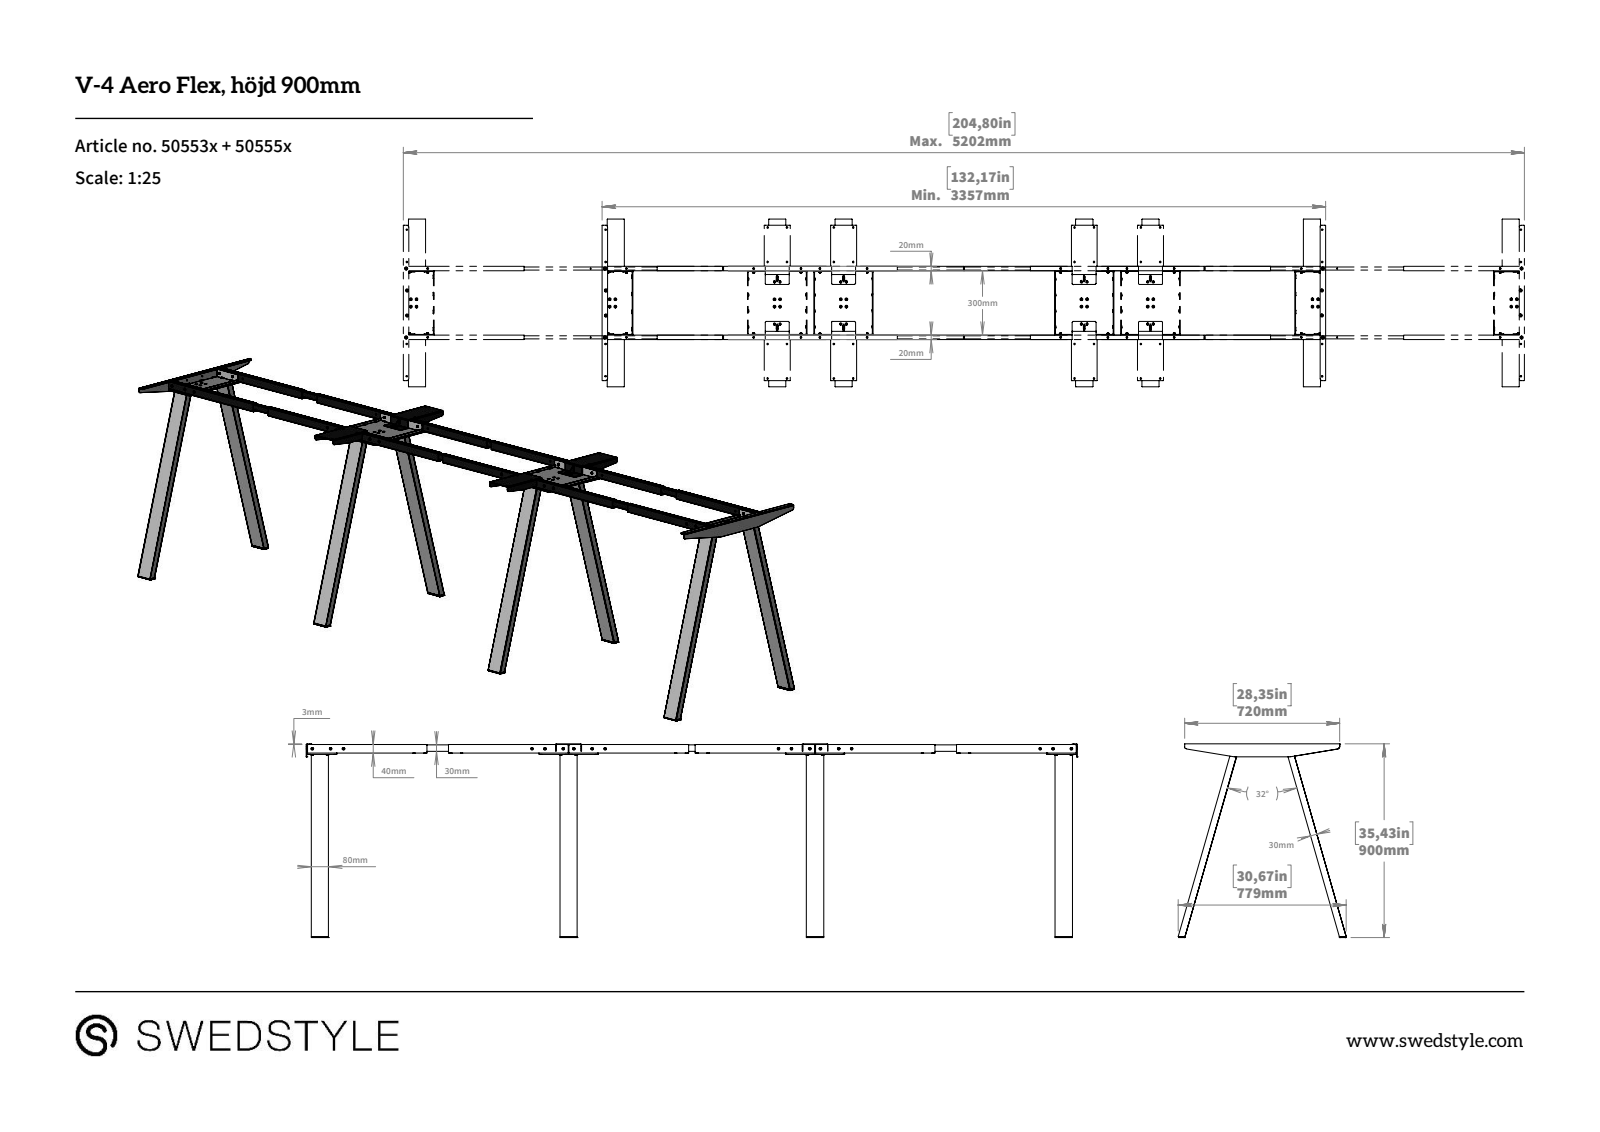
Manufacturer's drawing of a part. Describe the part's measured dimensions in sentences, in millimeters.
The part is named "V-4 Aero Flex_höjd 900_50553x+50555x". Its 3-D file was written by "SolidWorks 2017 (CONFIG_CONTROL_DESIGN)". It is 0 solids with 1265 faces: 579 planar, 484 cylindrical and 202 other. Overall it measures 3578 by 899.33 by 778.99 millimeters. Round holes: 44 of diameter 7, 18 of diameter 5, 14 of diameter 6.8, 10 of diameter 12, 2 of diameter 7.5. Round bosses or shafts: 7 of diameter 10, 6 of diameter 11.34, 2 of diameter 11.65, 1 of diameter 6. Partial cylindrical surfaces (rounded edges, fillets, slot ends): 48 of radius 2, 44 of radius 1, 24 of radius 3, 20 of radius 3.5, 8 of radius 5, 6 of radius 1.5, 6 of radius 4.5, 4 of radius 8. The main face-to-face distances are 2, 319.2, 6, 18, 30, 20, 29.9, 30.09, 29.99, 46. The hole center spacings are 1214, 120, 320, 341.76, 26, 46.1, 62.57, 62.65.
